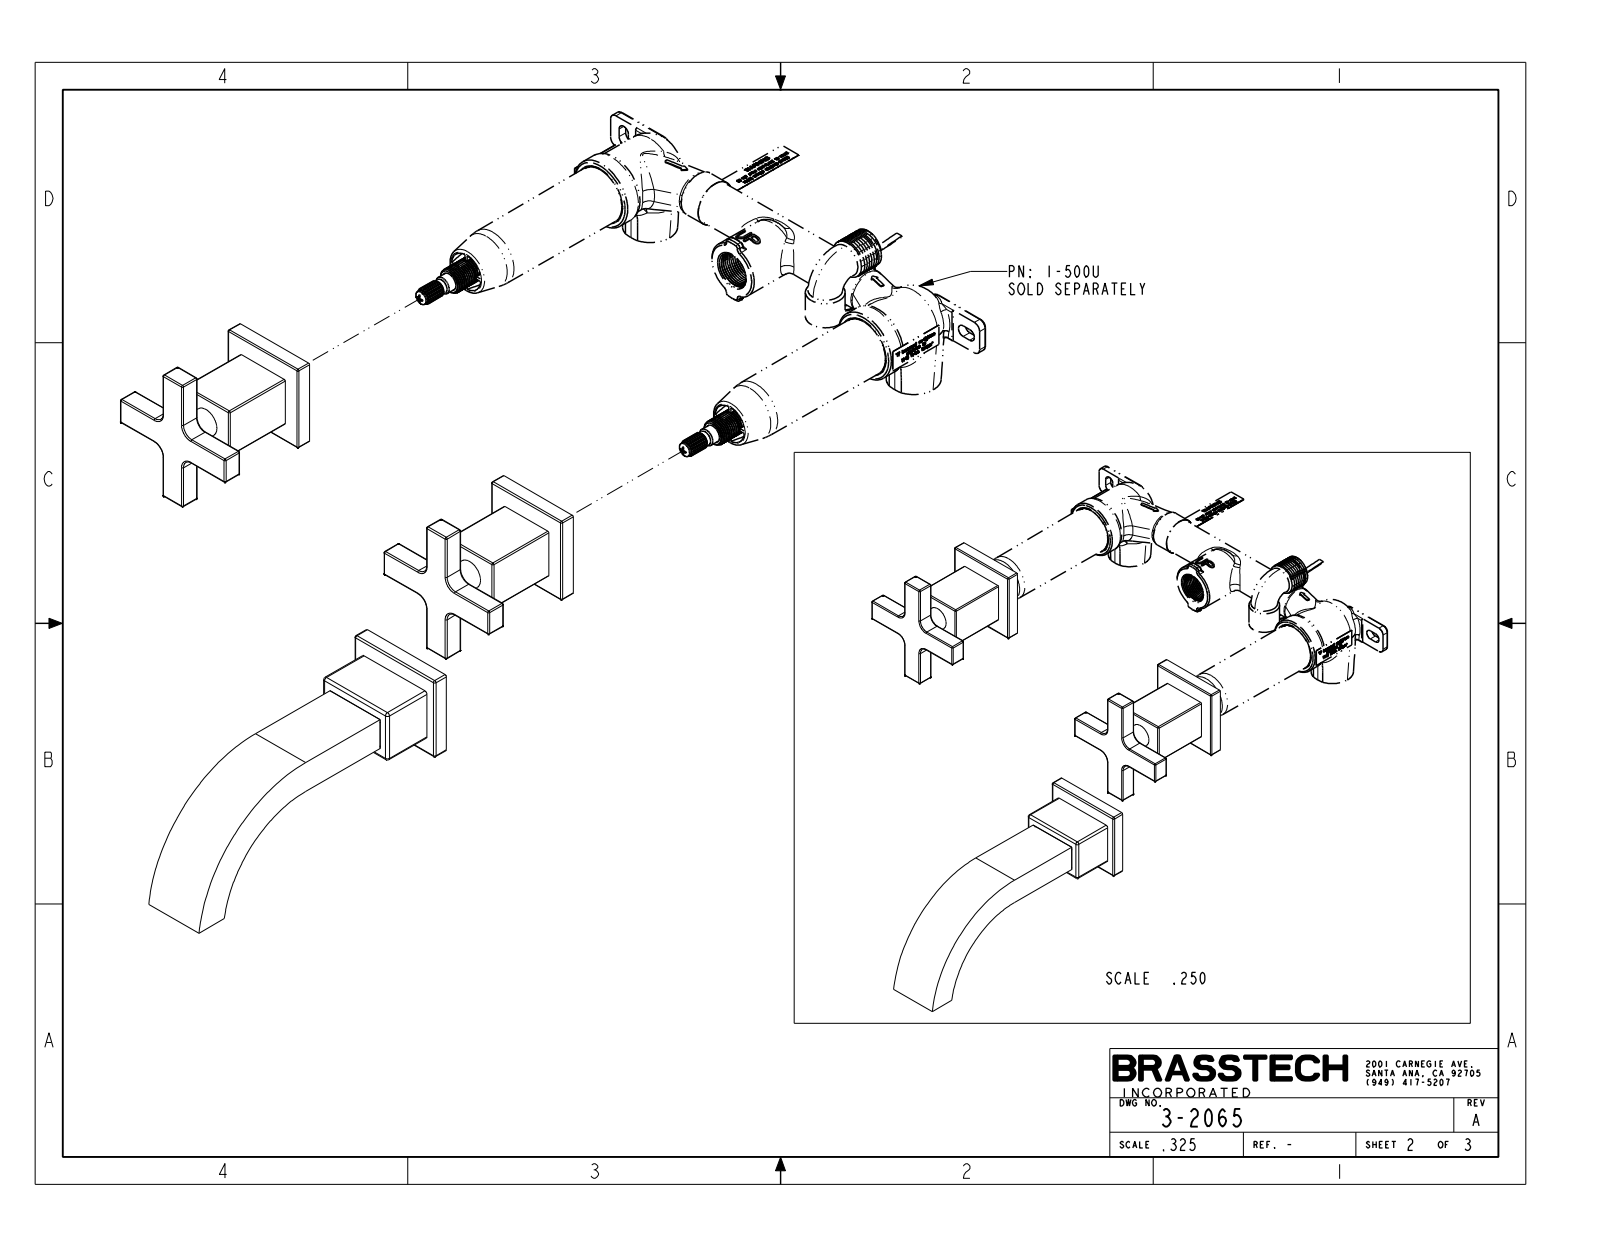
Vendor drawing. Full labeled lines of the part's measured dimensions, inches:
Part name (STEP PRODUCT): 3-2065_SW0001
STEP written by: CREO PARAMETRIC BY PTC INC, 2018400 (AUTOMOTIVE_DESIGN)
Units: inches
Bodies: 3 solids, 274 faces (68 planar, 130 cylindrical, 76 other)
Overall size (bounding box): 11.015 × 10.025 × 6.94
Volume: 23.17 in³ · Surface area: 112.3 in²
Round bosses / shafts (diameter × count): ⌀0.65 ×2, ⌀0.523 ×2
Partial cylindrical surfaces — rounded edges, fillets, slot ends (radius × count): R0.03 ×68, R0.04 ×8, R0.06 ×8, R0.25 ×8, R2.463 ×1, R3.213 ×1
Main face-to-face distances: 0.35, 0.45, 3.046, 2.696, 7.875, 2.596, 2.246, 1.5, 1.72, 1.16
